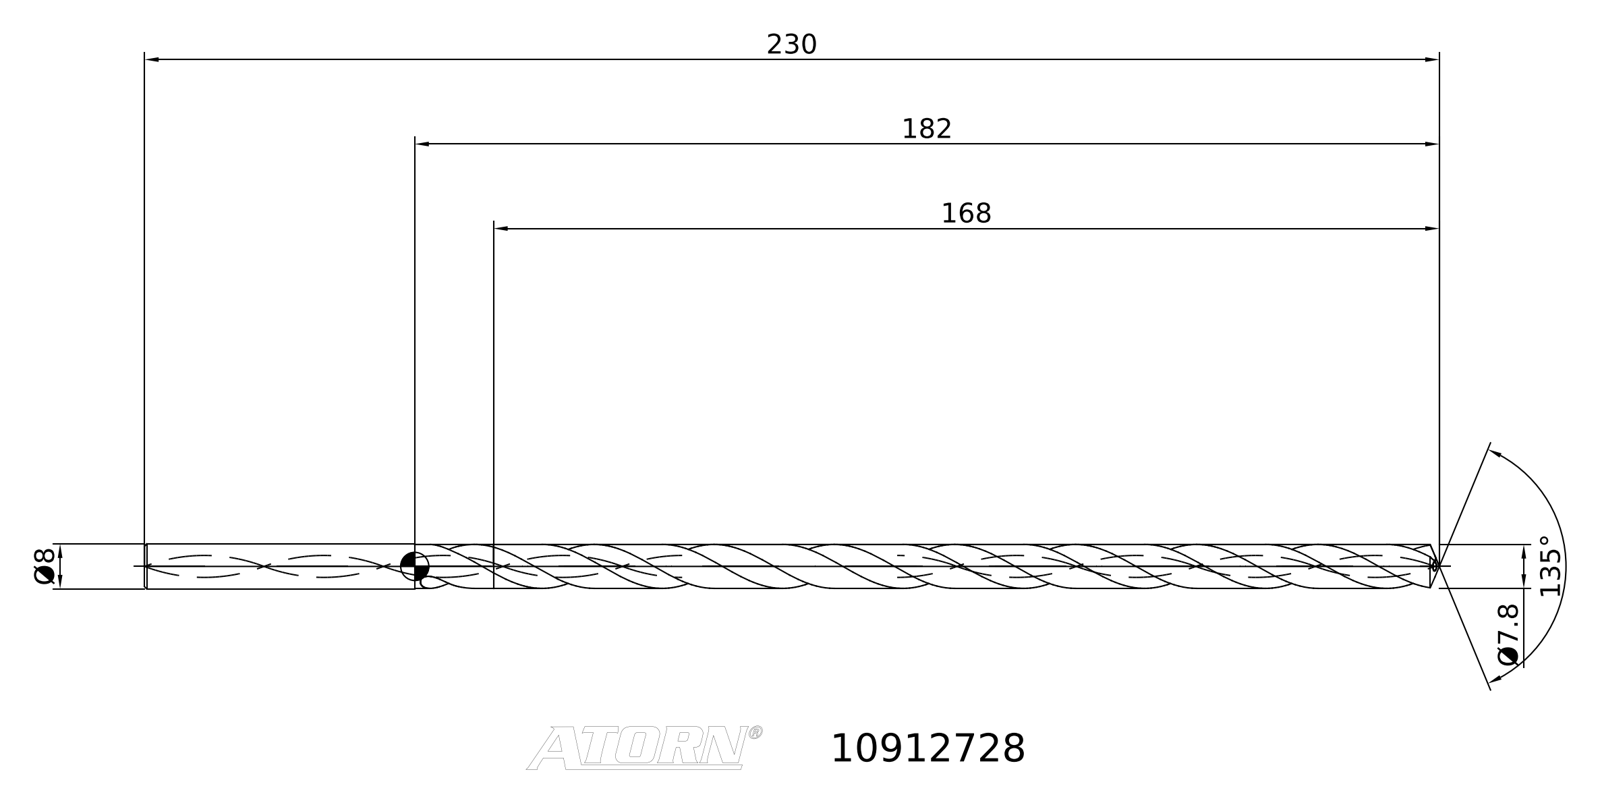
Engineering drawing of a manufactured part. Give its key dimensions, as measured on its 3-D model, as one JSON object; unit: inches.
{"step_written_by": "TDM (AUTOMOTIVE_DESIGN)", "units": "inches", "bodies": {"solids": 2, "faces": 37, "planar": 6, "cylindrical": 0, "other": 31}, "overall_size": [9.055, 0.477, 0.315], "volume_in3": 0.489, "surface_area_in2": 9.729, "face_to_face_distances": [2.441, 6.567, 9.007, 7.118, 0.551, 1.89]}
